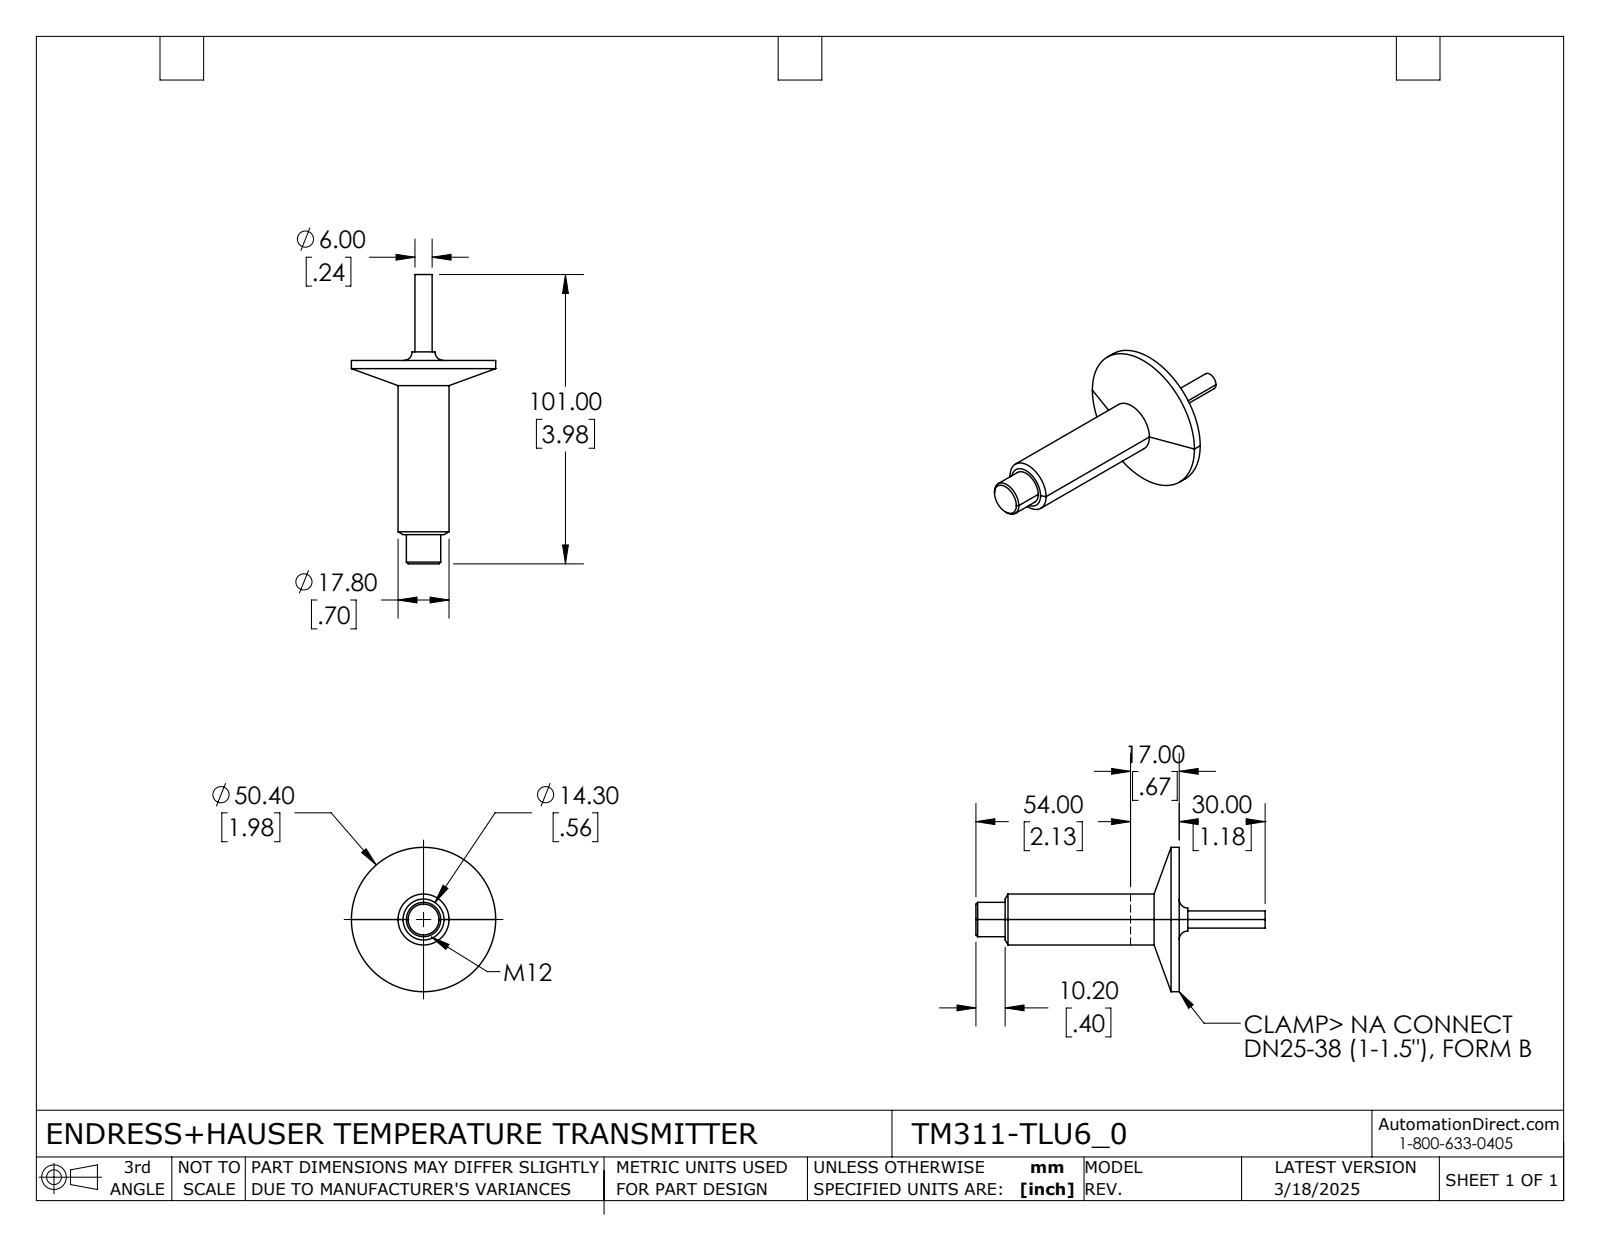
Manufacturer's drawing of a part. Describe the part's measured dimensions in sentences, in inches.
The part is named "TM311-TLU6_0". Its 3-D file was written by "SolidWorks 2021 (AUTOMOTIVE_DESIGN)". It is 1 solid with 29 faces: 6 planar, 8 cylindrical and 15 other. Overall it measures 3.976 by 1.984 by 1.984 inches. Its volume is 1.59 cubic inches and its surface area 13.31 square inches. Round bosses or shafts: 1 of diameter 1.984, 1 of diameter 0.701, 1 of diameter 0.472, 1 of diameter 0.236. The main face-to-face distances are 2.795, 2.394, 0.402, 1.181, 3.575, 3.976, 1.063, 0.118, 2.512, 2.913.
